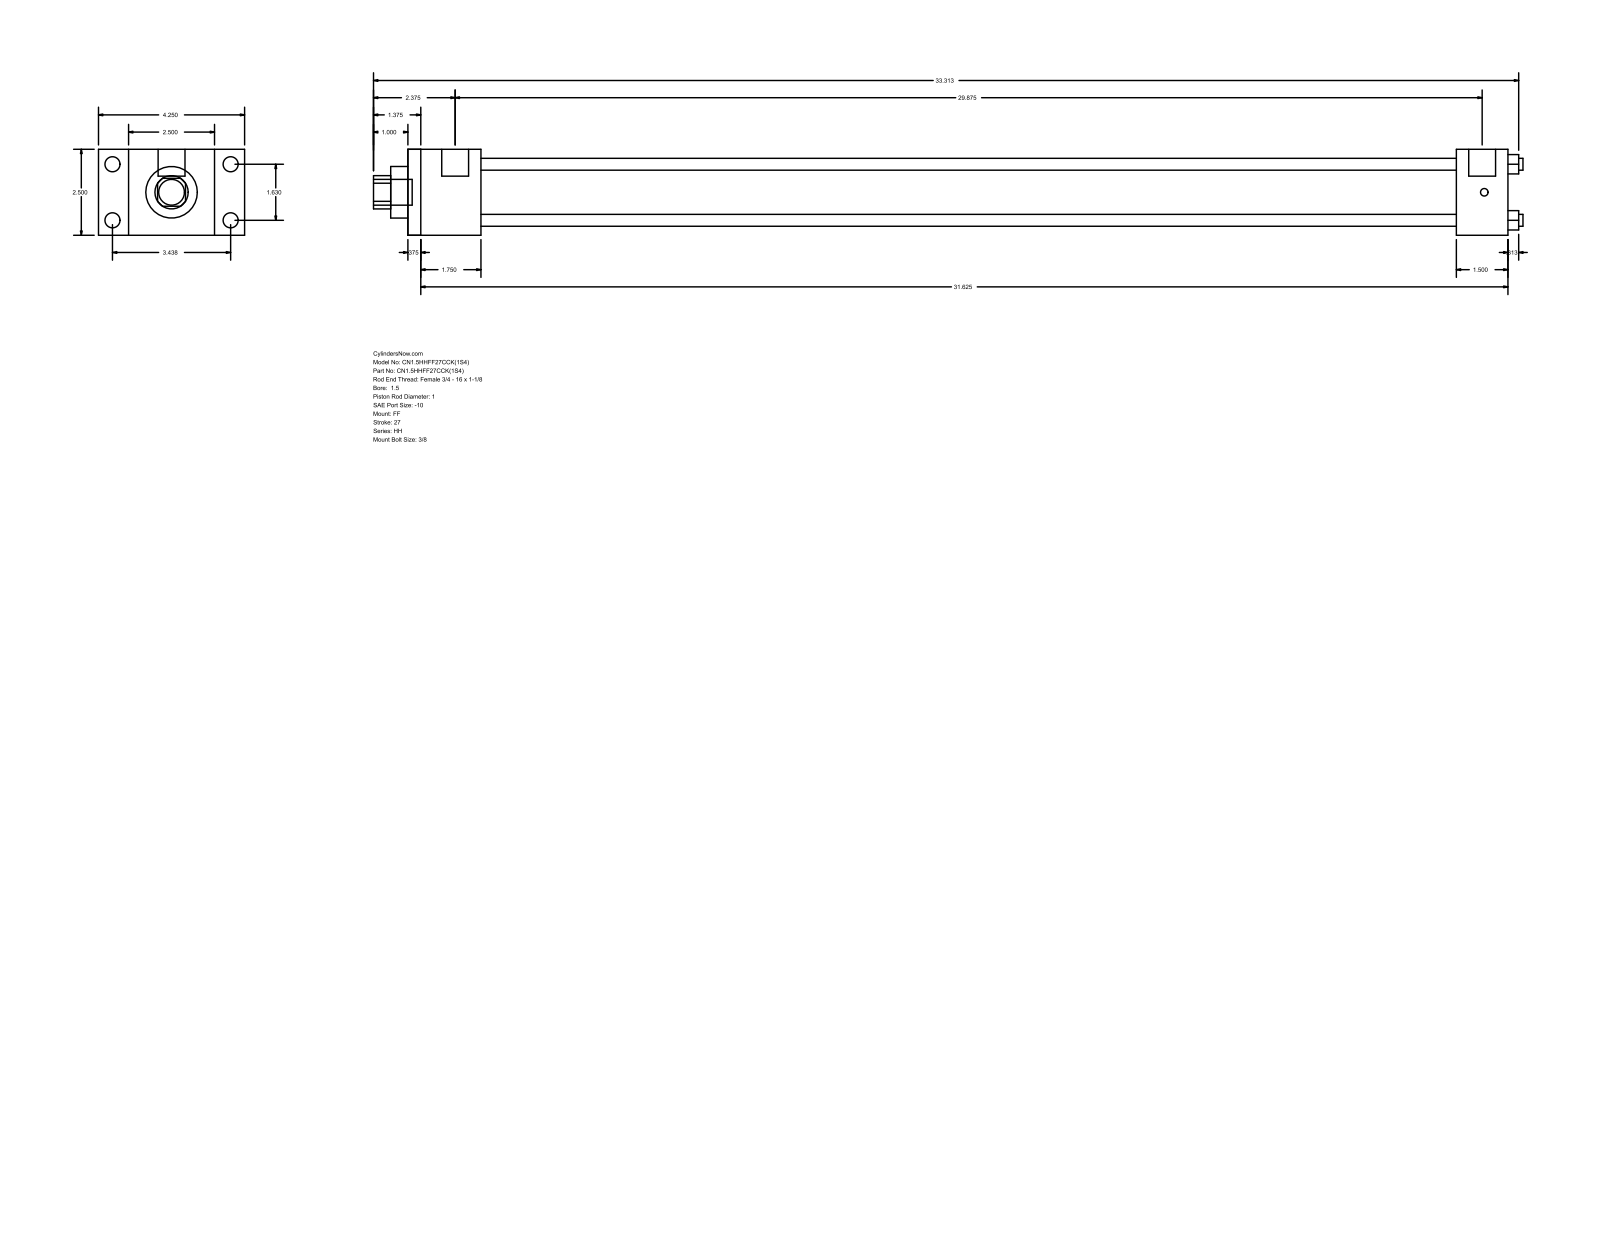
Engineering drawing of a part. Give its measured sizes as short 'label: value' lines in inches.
name: HH_FF__0150_1
written by: GSSL Pune (CONFIG_CONTROL_DESIGN)
unit: in
bodies: 0 solids, 92 faces (64 planar, 28 cylindrical, 0 other)
size: 33.437 × 4.25 × 2.5
holes: 4× ⌀0.345, 1× ⌀1, 1× ⌀1.5, 1× ⌀1.75
bosses: 4× ⌀0.438, 4× ⌀0.219, 2× ⌀0.781, 1× ⌀0.75
rounds: 1× R0.484
face distances: 2.5, 32, 0.375, 31.625, 2.125, 1.75, 29.875, 30.5, 30.125, 28.375
hole spacings: 1.152, 1.63, 2.305
